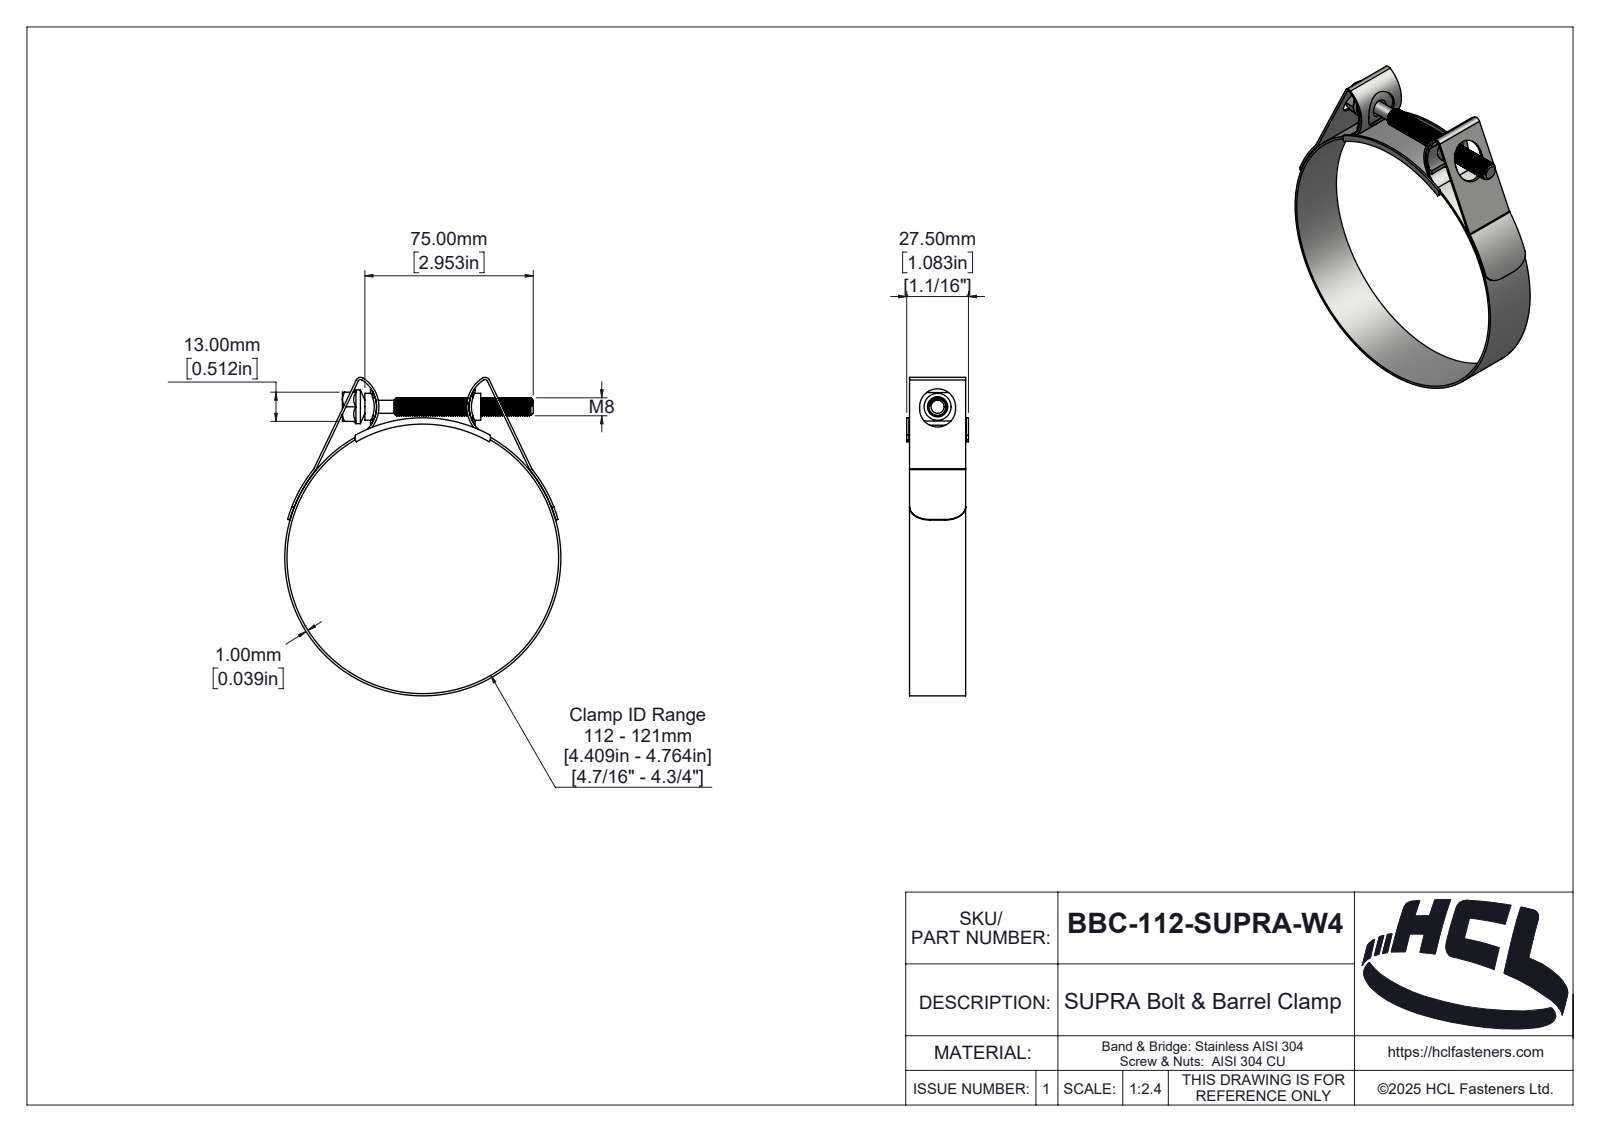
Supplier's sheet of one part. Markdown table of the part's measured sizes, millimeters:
| quantity | value |
| --- | --- |
| part name | BBC-112-SUPRA-W4 |
| STEP written by | SolidWorks 2025 (AUTOMOTIVE_DESIGN) |
| units | millimeters |
| bodies | 5 solids, 366 faces (46 planar, 233 cylindrical, 87 other) |
| overall size | 141.83 × 123 × 27.5 |
| volume | 19 836 mm³ |
| surface area | 35 304 mm² |
| round holes (diameter × count) | 121 × 1 |
| round bosses / shafts (diameter × count) | 123 × 1, 15.01 × 1, 12 × 1, 8 × 1, 5.8 × 1 |
| partial cylindrical surfaces (radius × count) | 1 × 4, 1.1 × 2, 2 × 2, 2.1 × 2, 3 × 2, 8 × 2, 13.03 × 2, 14.03 × 2 |
| main face-to-face distances | 1, 25, 1.25, 26.25, 26.5, 25.25, 27.5, 25.5, 13, 2.5 |
